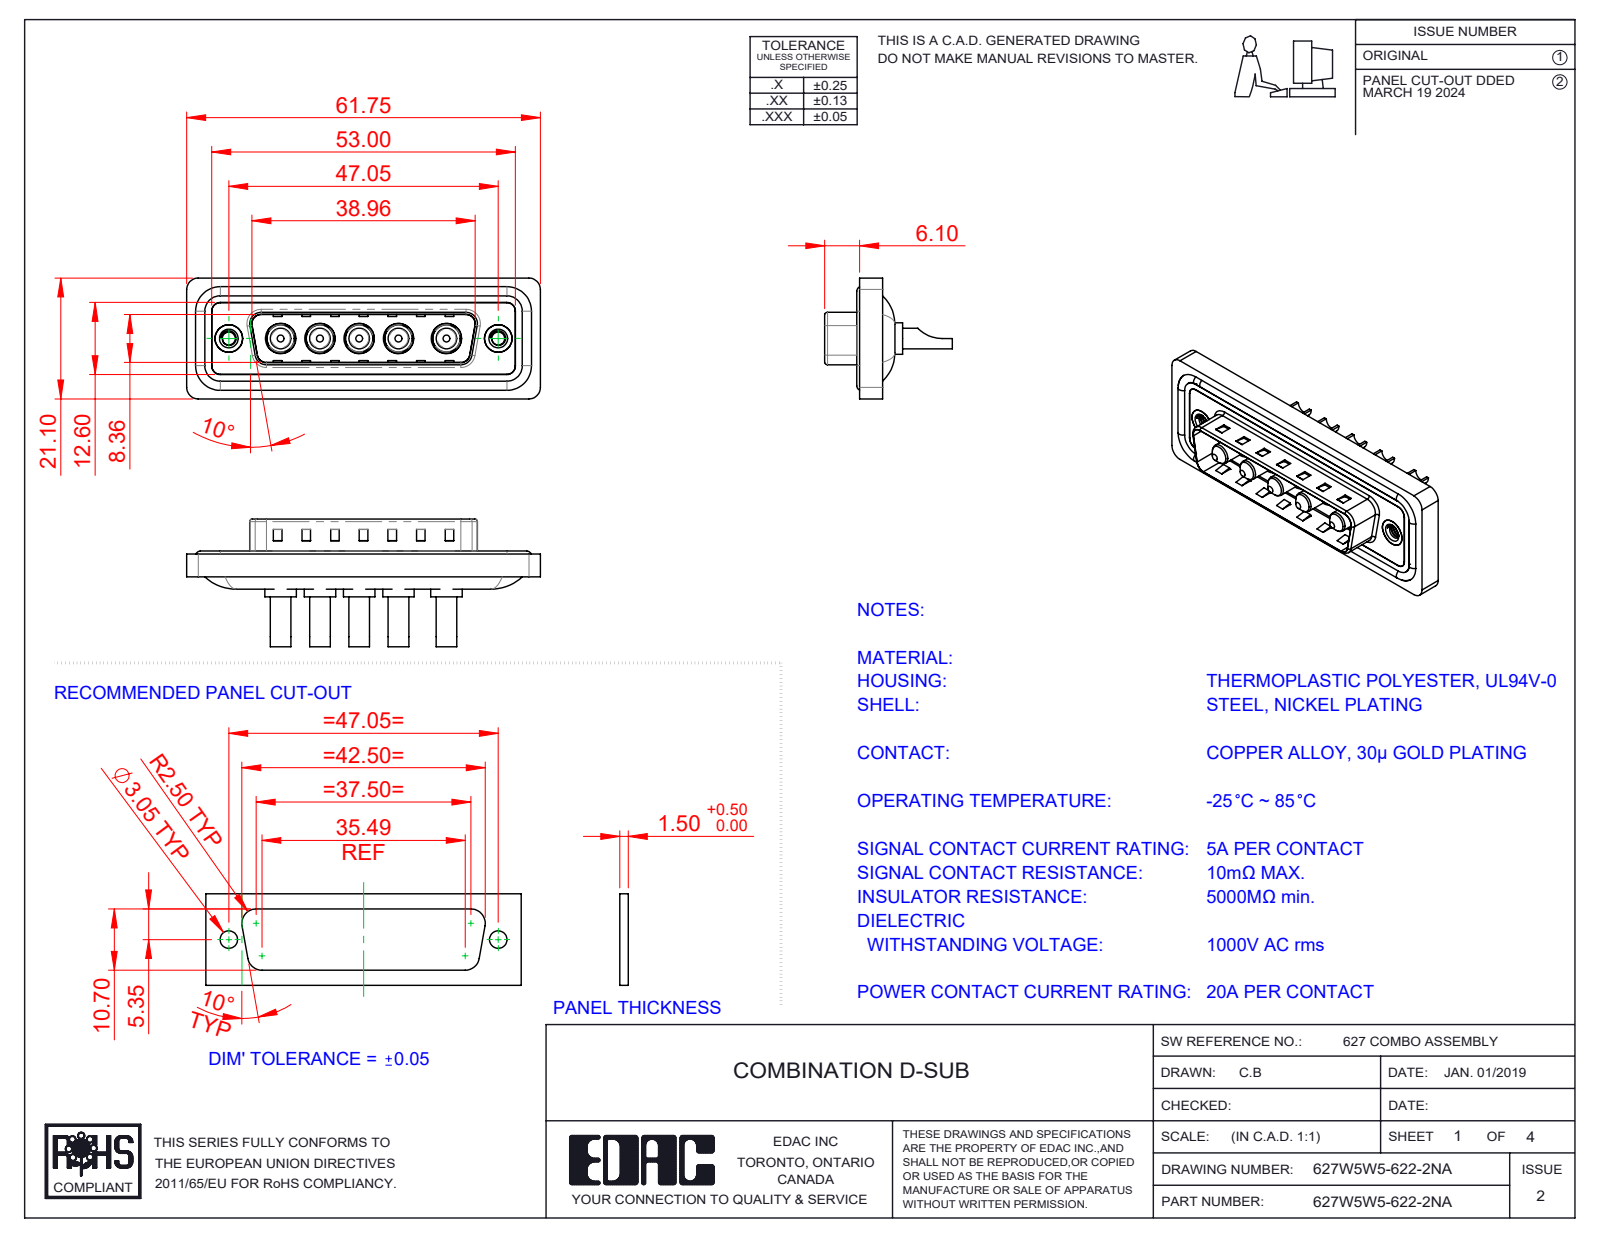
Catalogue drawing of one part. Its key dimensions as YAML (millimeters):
part_name: "627Combo Waterproof Housing_25 Contacts; 627Combo Housing_5W5; 627Combo Threaded Rivet_A; 627Combo Shell Rear_25 Contacts (+3 more)"
step_written_by: "SolidWorks 2023 (CONFIG_CONTROL_DESIGN)"
units: millimeters
bodies: {solids: 17, faces: 711, planar: 274, cylindrical: 300, other: 137}
overall_size: [61.75, 22.3, 21.1]
volume: 7539
surface_area: 12206
round_holes:
  - {diameter: 2.7, count: 5}
  - {diameter: 4.85, count: 5}
  - {diameter: 5.3, count: 5}
  - {diameter: 2.26, count: 2}
  - {diameter: 4, count: 2}
  - {diameter: 4.8, count: 2}
  - {diameter: 5, count: 2}
round_bosses_or_shafts:
  - {diameter: 5.5, count: 5}
  - {diameter: 5.2, count: 5}
  - {diameter: 4.75, count: 5}
  - {diameter: 3.75, count: 5}
  - {diameter: 3.6, count: 5}
  - {diameter: 1.6, count: 4}
  - {diameter: 4.9, count: 2}
partial_cylinders:
  - {radius: 1.5, count: 22}
  - {radius: 2, count: 18}
  - {radius: 0.5, count: 8}
  - {radius: 1.6, count: 8}
  - {radius: 2.1, count: 5}
  - {radius: 0.25, count: 4}
  - {radius: 0.6, count: 4}
  - {radius: 0.65, count: 4}
face_to_face_distances: [0.4, 1.5, 0.5, 1.1, 3.1, 1.6, 2.9, 0.82, 9.58, 5.65]
hole_center_spacings: [6.86, 9.04, 13.73, 38.01, 6.87, 8.37, 8.38, 9.05]
